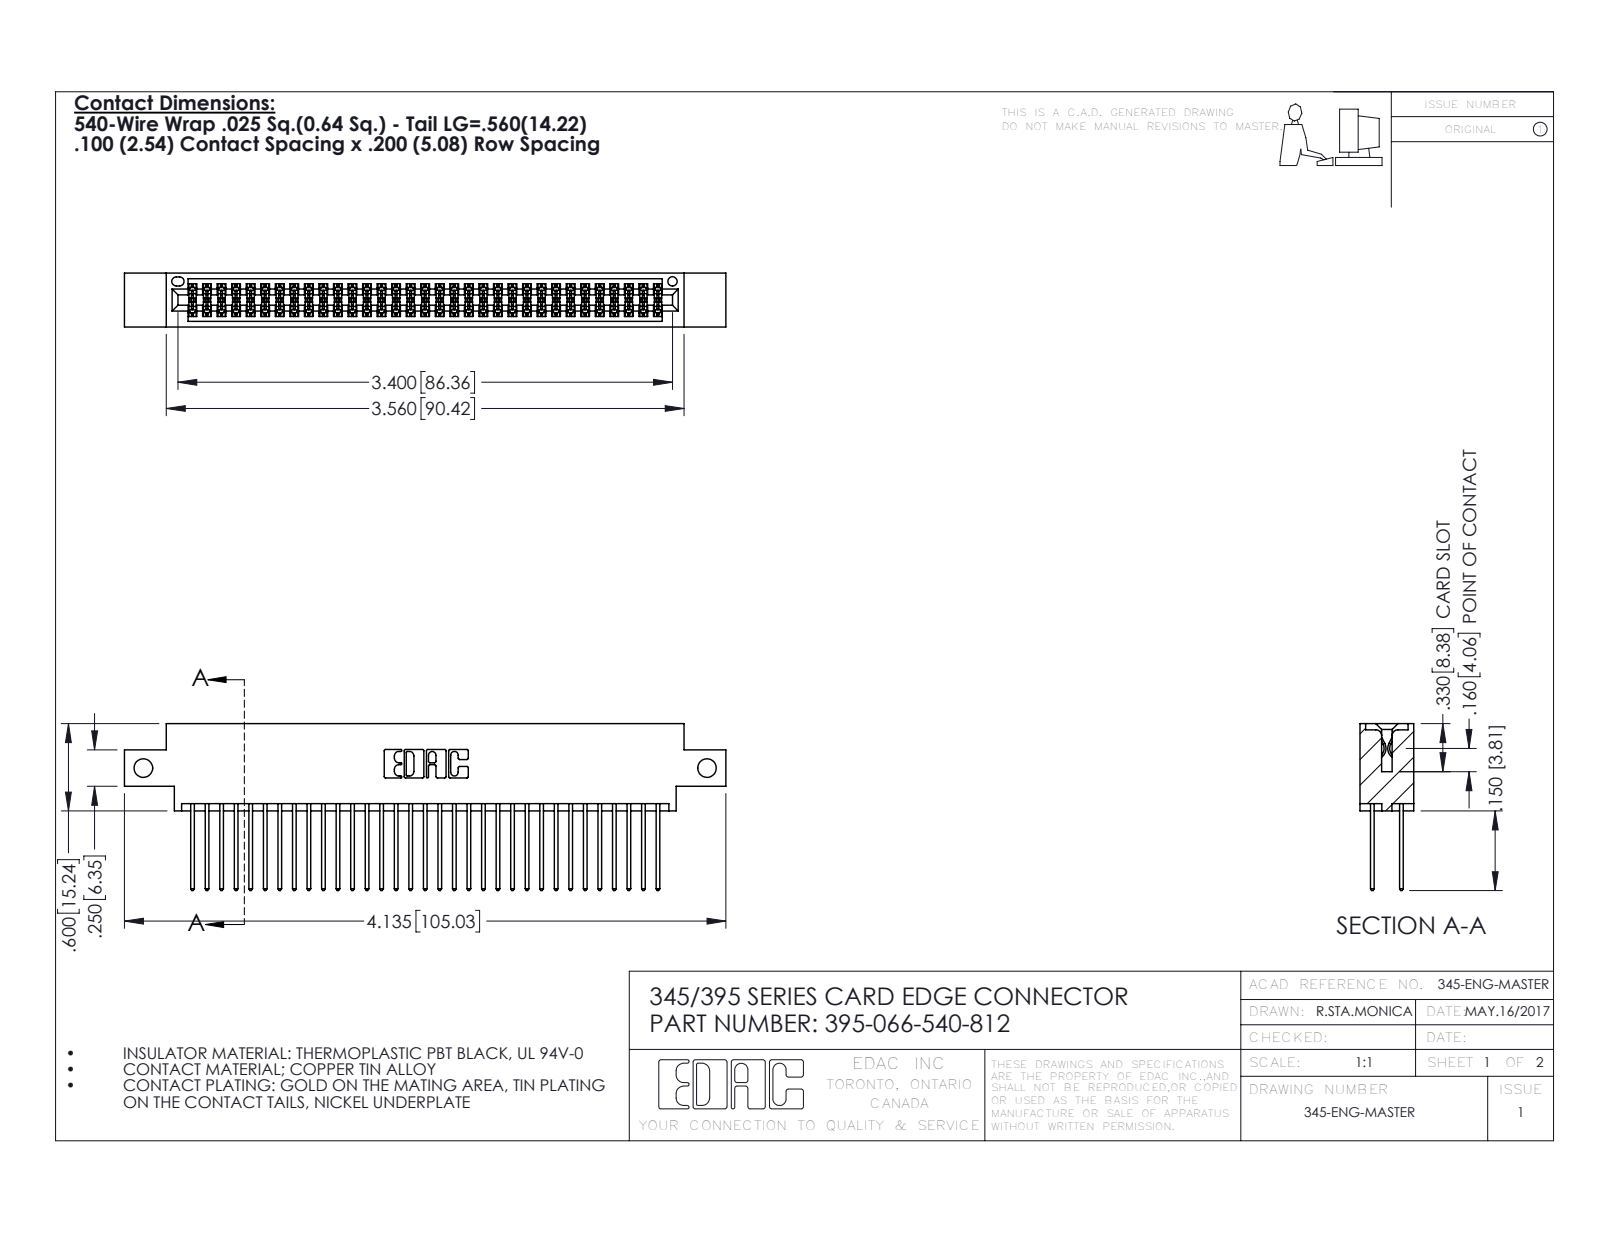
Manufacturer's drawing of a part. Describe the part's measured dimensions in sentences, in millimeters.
The part is named "395-066-540-812; 345 Part_0.170 Offset - Side Mount; 345-292-001_345-293-140". Its 3-D file was written by "SolidWorks 2016 (CONFIG_CONTROL_DESIGN)". It is 67 solids with 3430 faces: 2262 planar, 1168 cylindrical and 0 other. Overall it measures 105 by 29.1 by 9.4 millimeters. Its volume is 10 200 cubic millimeters and its surface area 16 030 square millimeters. Round holes: 2 of diameter 3.3, 1 of diameter 1.6. Partial cylindrical surfaces (rounded edges, fillets, slot ends): 99 of radius 0.2, 66 of radius 0.3, 22 of radius 0.3, 6 of radius 0.2, 6 of radius 0.8, 3 of radius 0.7, 2 of radius 0.4, 2 of radius 0.5. The main face-to-face distances are 7.6, 1.8, 5.1, 2.5, 6.9, 0.6, 9.4, 5.7, 4.4, 3.8. The hole center spacings are 98.4.
